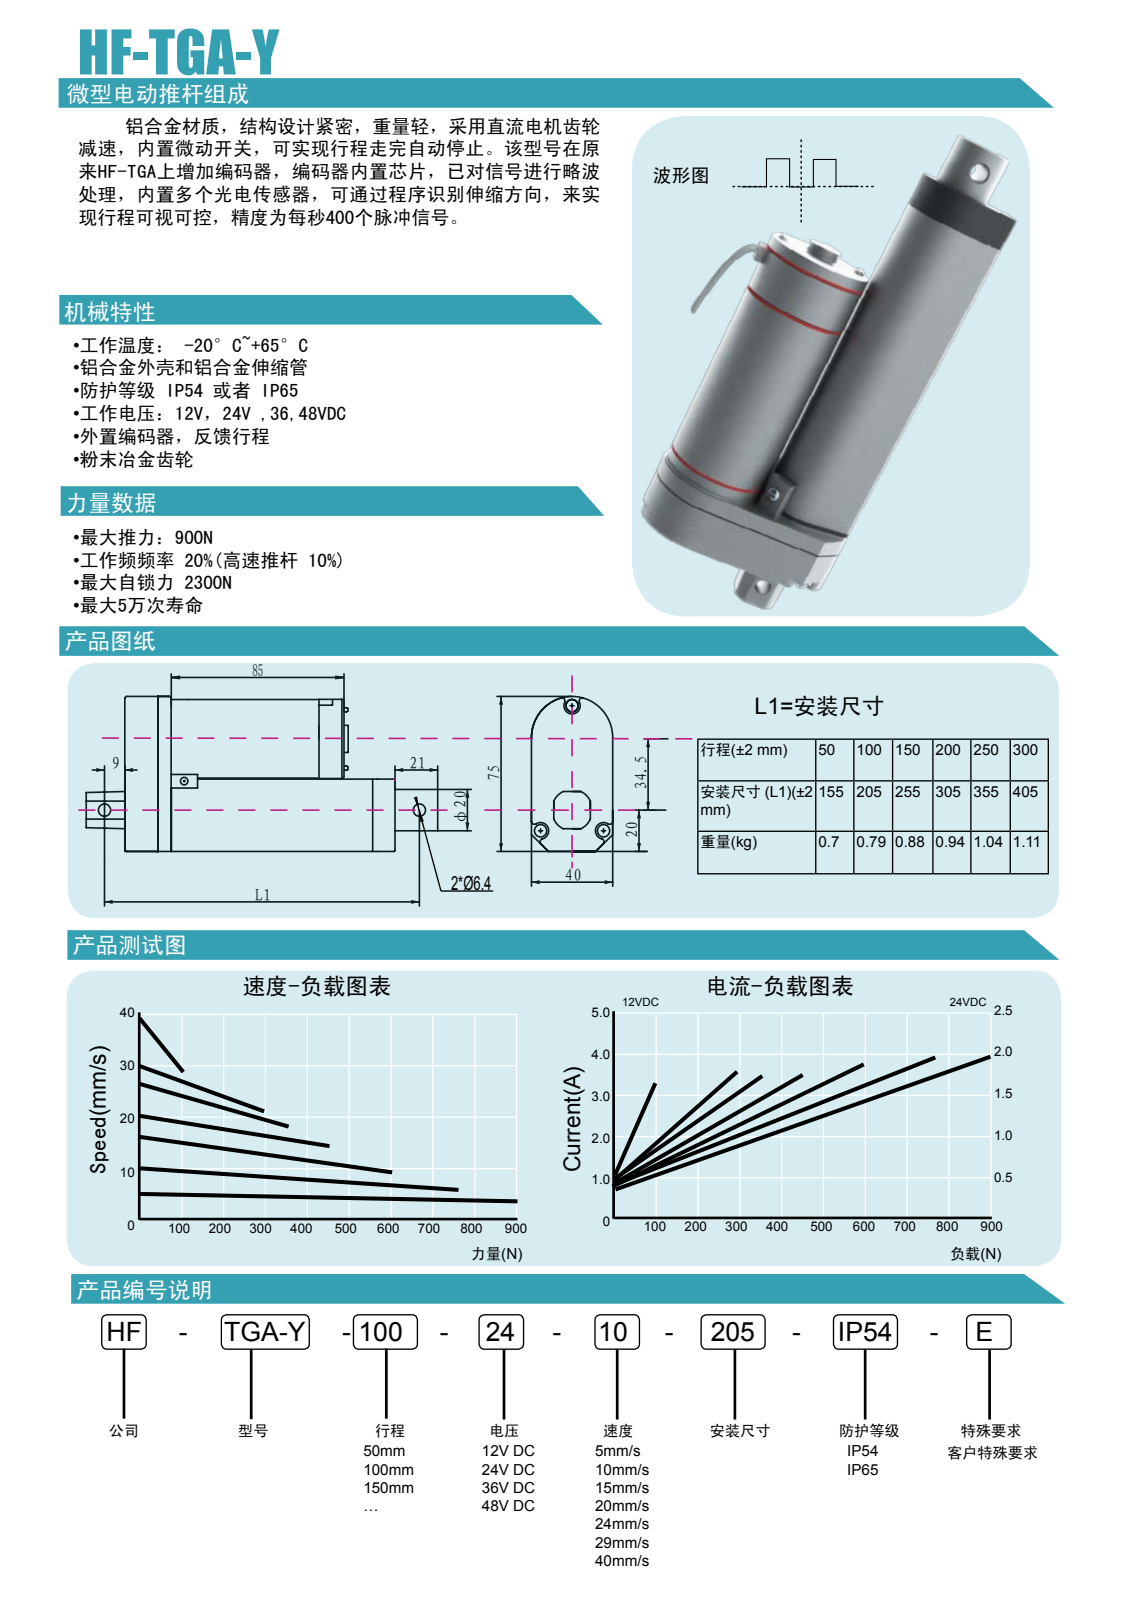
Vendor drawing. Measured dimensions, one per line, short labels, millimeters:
name: UP; END; MOTER; WAIKE (+3 more)
written by: PRO/ENGINEER BY PARAMETRIC TECHNOLOGY CORPORATION, 2008380 (CONFIG_CONTROL_DESIGN)
unit: mm
bodies: 6 solids, 380 faces (187 planar, 98 cylindrical, 95 other)
size: 223 × 75.01 × 40.05
volume: 236 443 mm³; area: 77 387 mm²
holes: 2× ⌀6, 1× ⌀20, 1× ⌀35
bosses: 4× ⌀0.5, 3× ⌀6, 2× ⌀5, 1× ⌀38, 1× ⌀13, 1× ⌀12.5, 1× ⌀3.2
rounds: 29× R1, 12× R0.5, 3× R4, 1× R10, 1× R13, 1× R14.99, 1× R17, 1× R19.5
face distances: 2, 16.3, 6.5, 22.8, 98.5, 13.5, 105, 121.3, 123.3, 109.8
hole spacings: 35, 205
